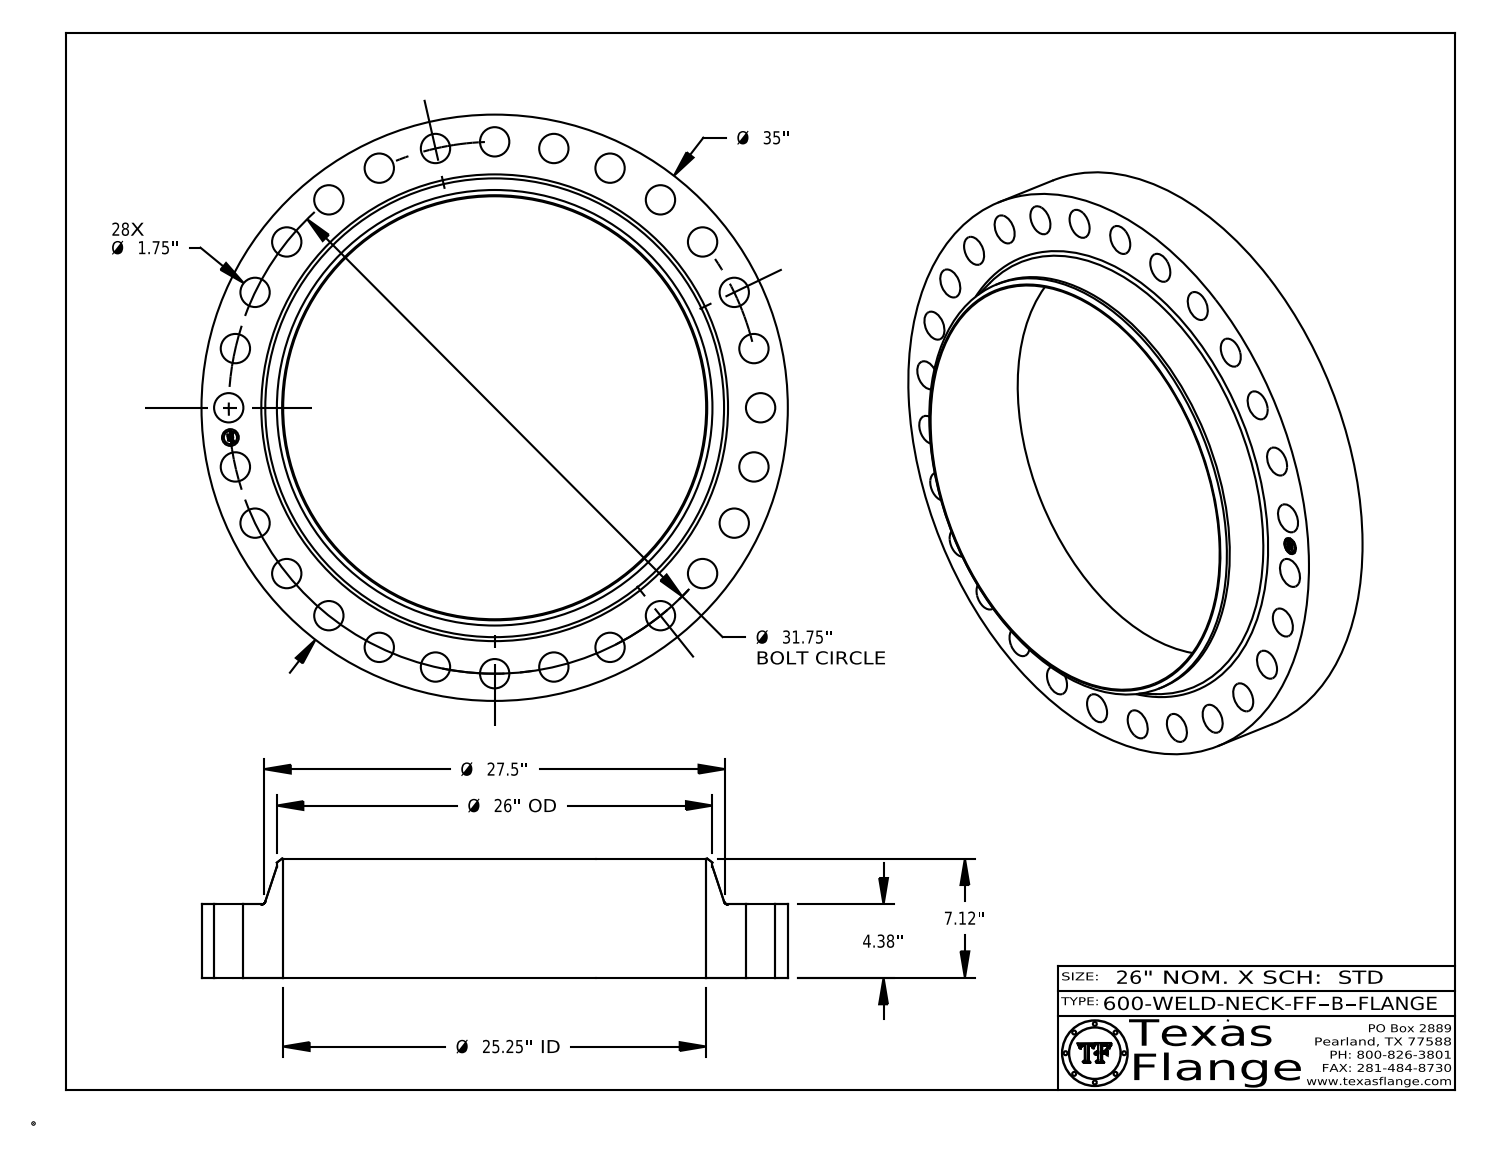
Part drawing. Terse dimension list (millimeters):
name: 600-WELD-NECK-FF, Series B
written by: CATIA V5 STEP AP214 (AUTOMOTIVE_DESIGN)
unit: mm
bodies: 1 solid, 456 faces (368 planar, 82 cylindrical, 6 other)
size: 889 × 889 × 180.8
volume: 30 760 000 mm³; area: 1 721 000 mm²
holes: 28× ⌀44.5, 1× ⌀25.4, 1× ⌀641.4
bosses: 8× ⌀1.5, 1× ⌀889, 1× ⌀660.4, 1× ⌀20
face distances: 111.3, 180.8, 69.6, 0.4, 110.9, 70, 7.6, 7.4, 1.4, 4.9
hole spacings: 429.1, 726.6, 761.2, 786.2, 349.9, 502.8, 90.3, 179.5
